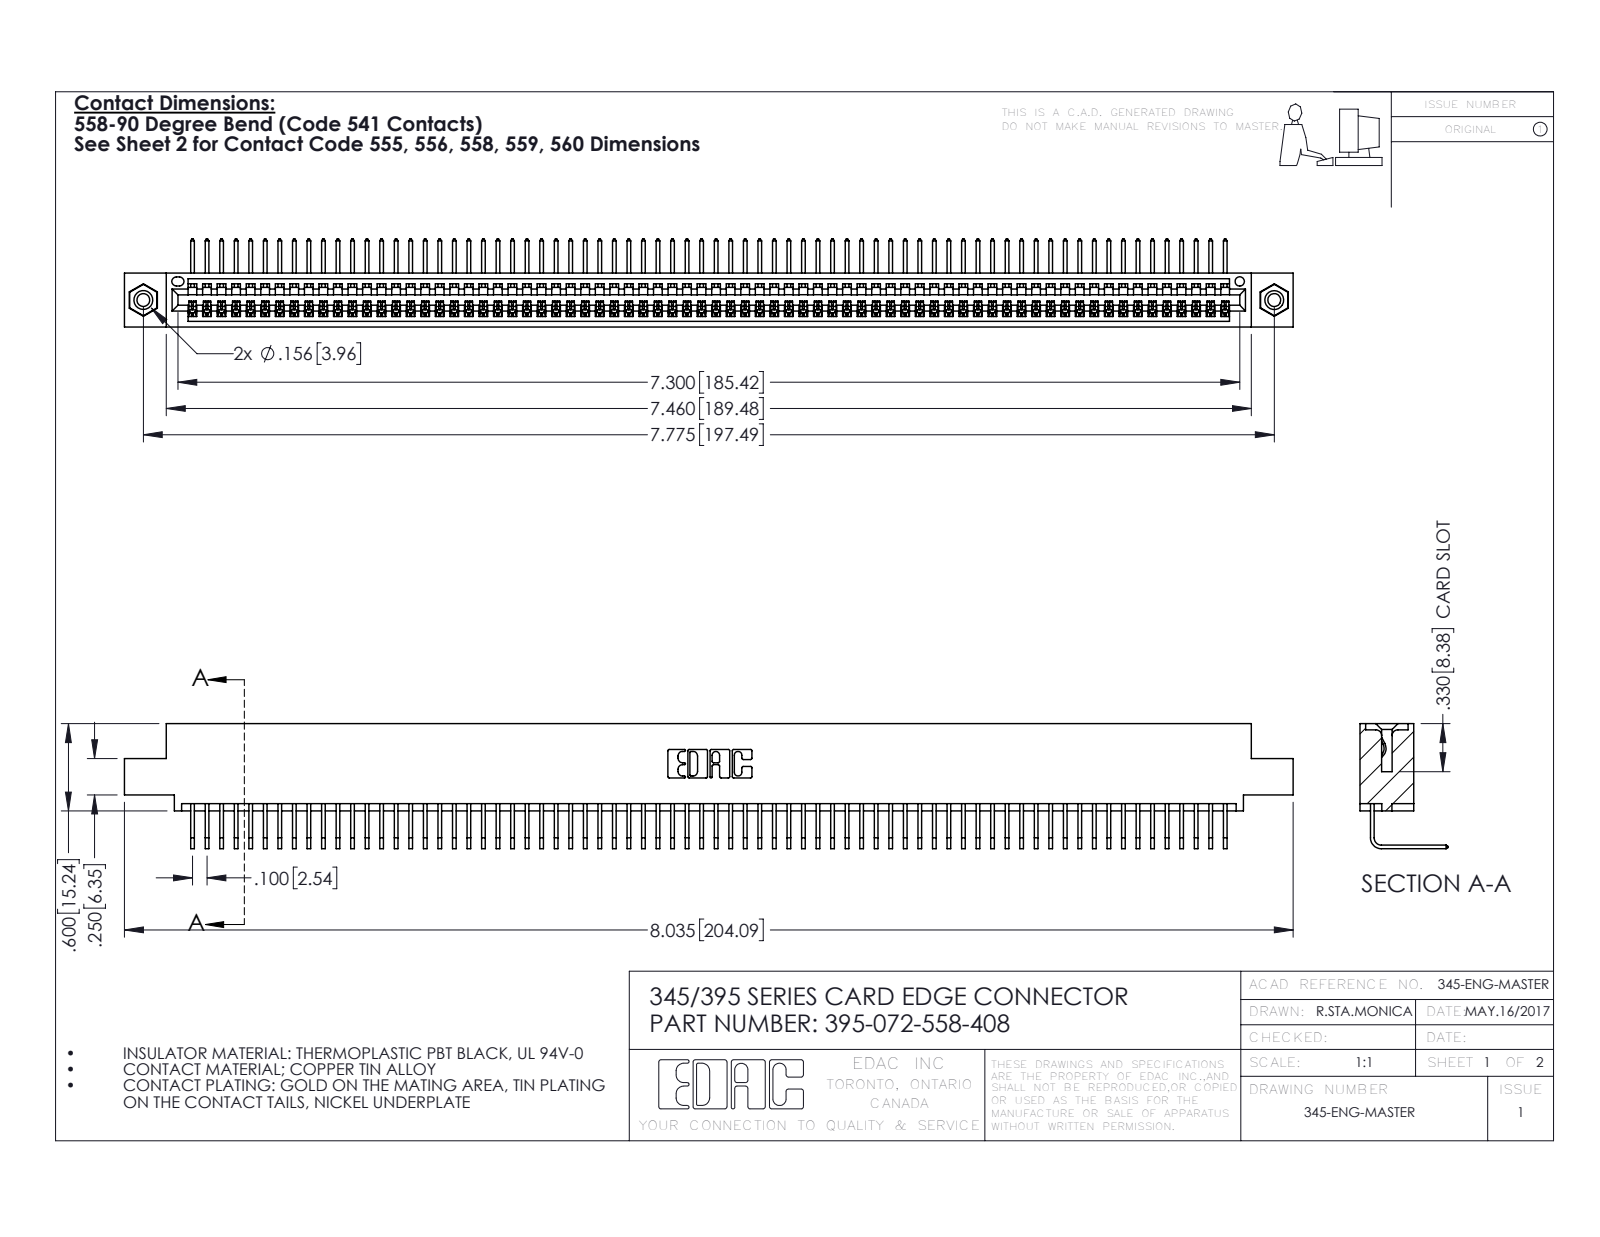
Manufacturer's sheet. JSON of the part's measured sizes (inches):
{"part_name": "345-292-001_558 Tail - 2; 345 Part_0.110 Offset - 0.156 Dia-TI; 395-072-558-408; 345-250-001_345-250-003-102", "step_written_by": "SolidWorks 2016 (CONFIG_CONTROL_DESIGN)", "units": "inches", "bodies": {"solids": 75, "faces": 4510, "planar": 3140, "cylindrical": 1354, "other": 16}, "overall_size": [8.035, 0.859, 0.605], "volume_in3": 1.208, "surface_area_in2": 43.74, "round_holes": [[0.089, 2], [0.125, 2], [0.156, 2], [0.064, 1]], "round_bosses_or_shafts": [[0.155, 2]], "partial_cylinders_radius": [[0.006, 144], [0.01, 22], [0.007, 6], [0.031, 6], [0.026, 3], [0.031, 2], [0.04, 2], [0.014, 1]], "face_to_face_distances": [0.072, 0.298, 0.37, 0.2, 0.098, 0.272, 0.025, 0.225, 0.149, 0.072], "hole_center_spacings": [0.27, 7.539, 7.775]}
